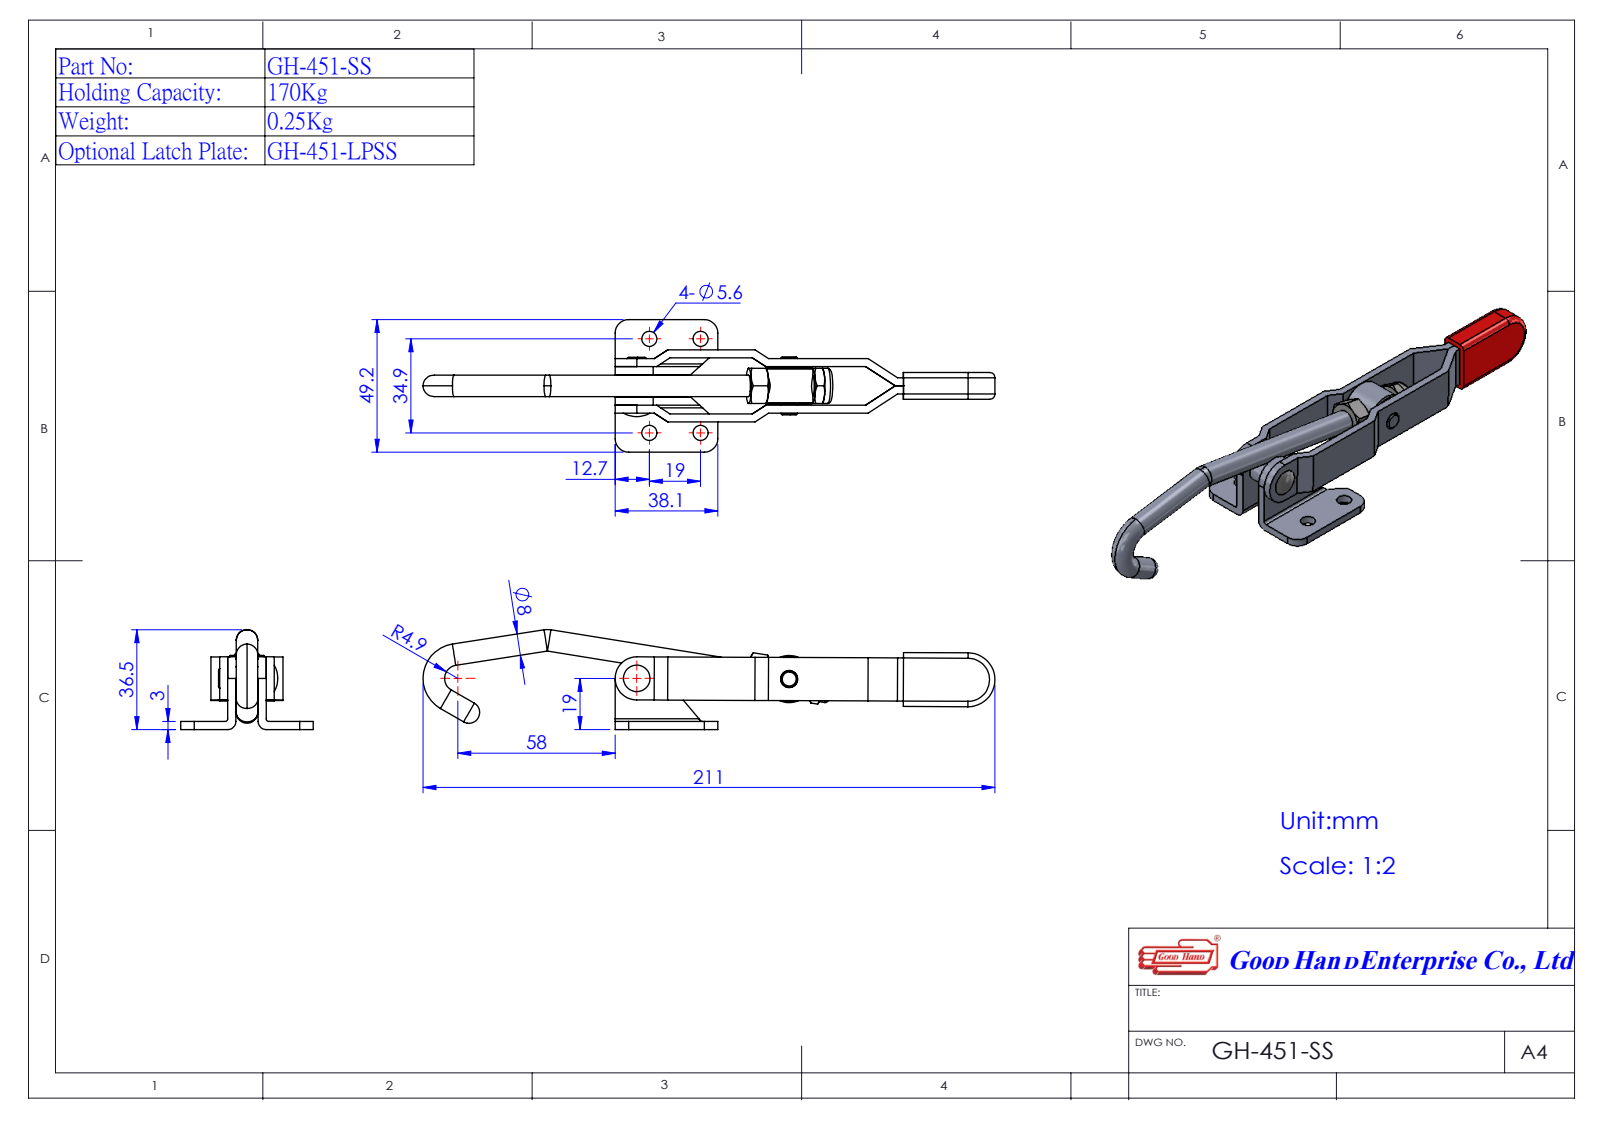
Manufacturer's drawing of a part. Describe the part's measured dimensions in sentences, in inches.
The part is named "Group3^493794(GH-451); Group2^493794(GH-451); Group1^493794(GH-451); 445144-1^493794(GH-451) (+1 more)". Its 3-D file was written by "SolidWorks 2016 (AUTOMOTIVE_DESIGN)". It is 6 solids with 171 faces: 81 planar, 56 cylindrical and 34 other. Overall it measures 7.842 by 1.937 by 1.38 inches. Its volume is 2.26 cubic inches and its surface area 37.52 square inches. Round holes: 4 of diameter 0.22, 2 of diameter 0.197, 2 of diameter 0.315, 1 of diameter 0.268, 1 of diameter 0.371. Round bosses or shafts: 3 of diameter 0.315, 1 of diameter 0.689, 1 of diameter 0.512, 1 of diameter 0.374. Partial cylindrical surfaces (rounded edges, fillets, slot ends): 4 of radius 0.197, 1 of radius 0.315, 1 of radius 0.394. The main face-to-face distances are 0.117, 0.118, 0.128, 0.807, 0.68, 0.201, 0.595, 0.085, 0.478, 0.563. The hole center spacings are 0.748, 1.374, 1.565, 2.228.
